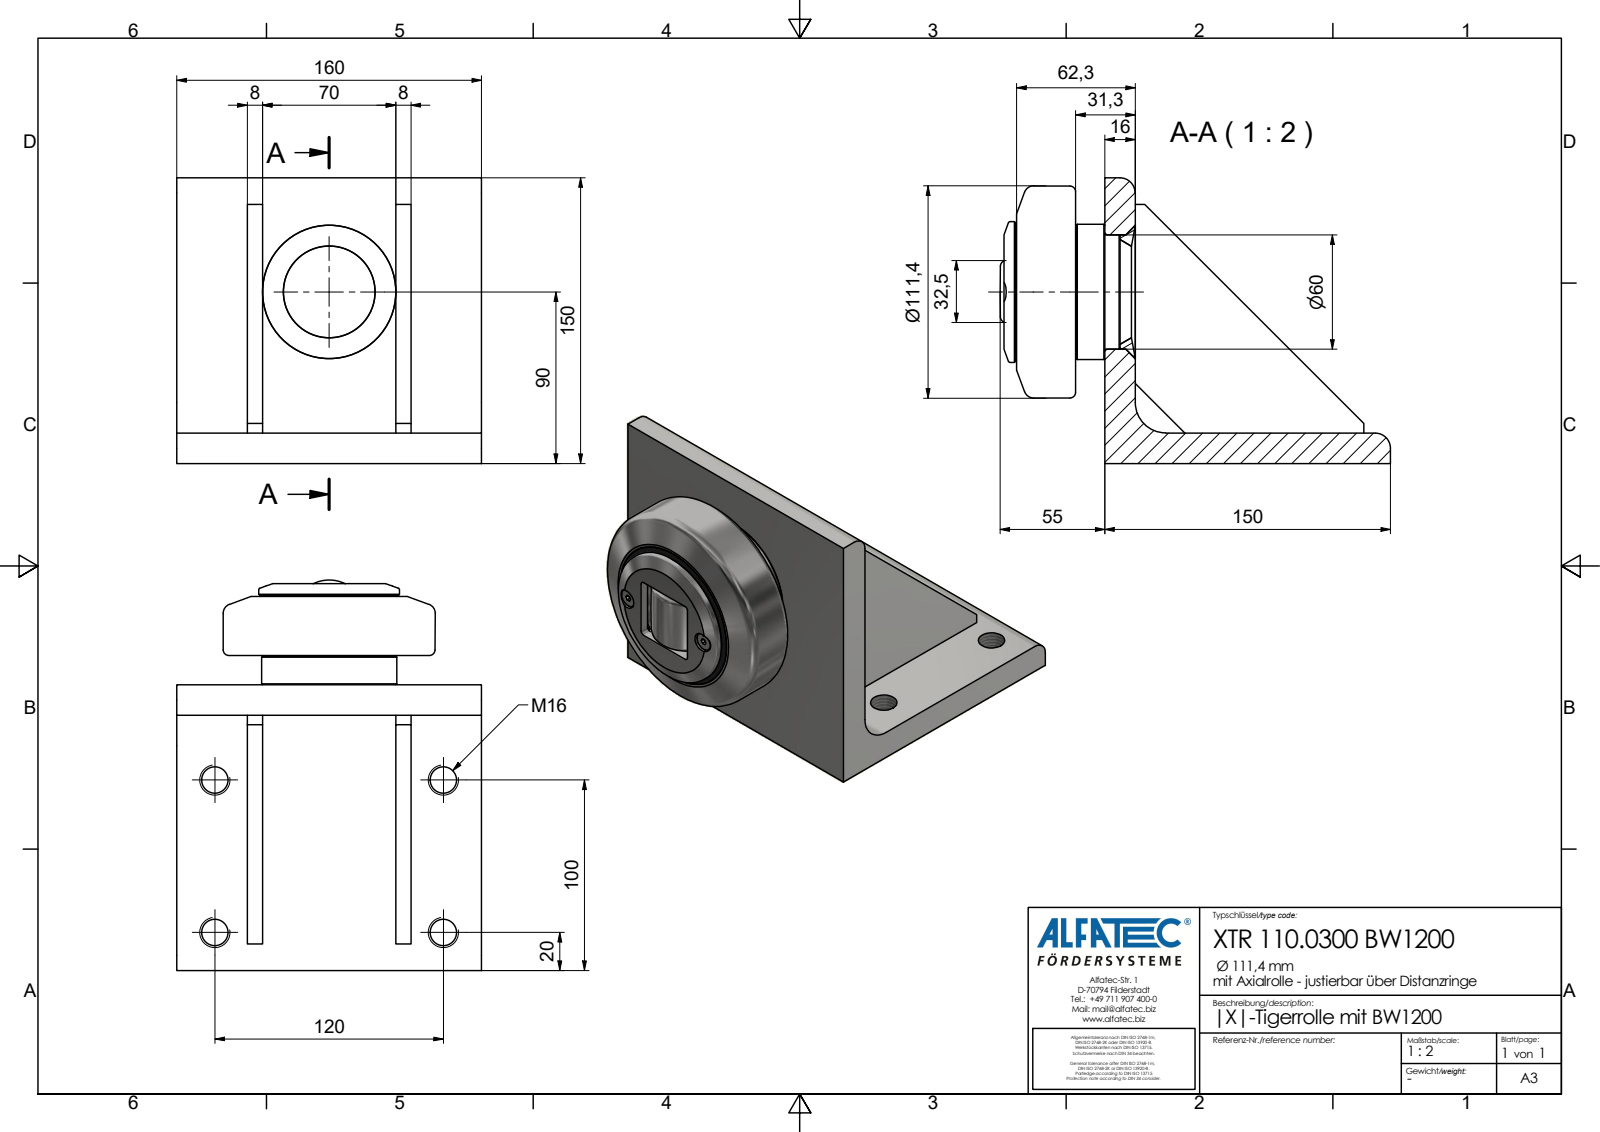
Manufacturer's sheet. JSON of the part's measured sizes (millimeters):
{"part_name": "XTR 110.0300 BW1200_Kontur", "step_written_by": "Autodesk Inventor 2020 (AP242_MANAGED_MODEL_BASED_3D_ENGINEERING_MIM_LF)", "units": "millimeters", "bodies": {"solids": 1, "faces": 99, "planar": 54, "cylindrical": 27, "other": 18}, "overall_size": [204.95, 160, 150], "volume_mm3": 1214000, "surface_area_mm2": 161586, "round_holes": [[13.84, 4], [10.5, 2]], "round_bosses_or_shafts": [[9.75, 2], [74, 1], [71.6, 1], [71, 1], [70.5, 1]], "partial_cylinders_radius": [[2, 4], [8, 2], [11.5, 1], [14, 1], [16, 1], [24, 1]], "face_to_face_distances": [16, 8, 78, 37, 45, 115, 123, 86, 70, 31.3], "hole_center_spacings": [80, 120, 144.22, 56]}
